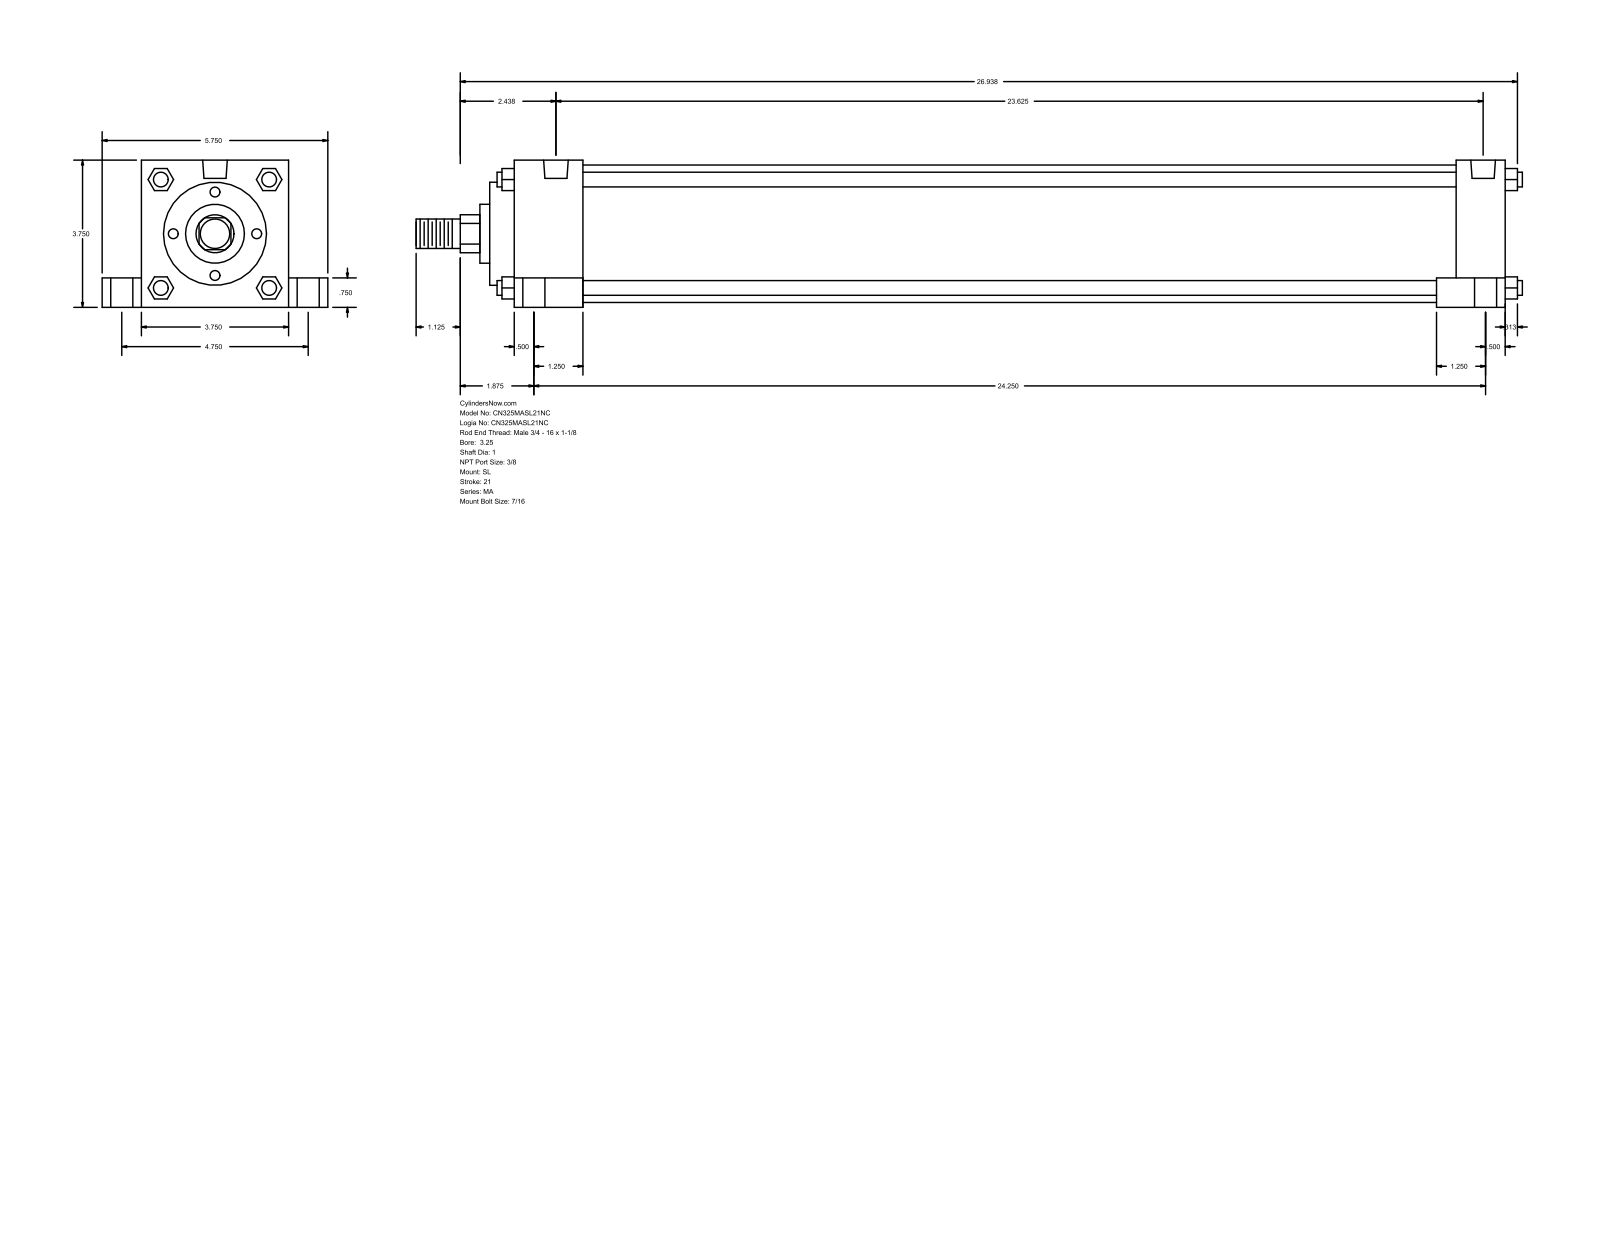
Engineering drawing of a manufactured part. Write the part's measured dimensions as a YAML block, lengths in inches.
part_name: "MA_SL__0325_1"
step_written_by: "GSSL Pune (CONFIG_CONTROL_DESIGN)"
units: inches
bodies: {solids: 0, faces: 150, planar: 113, cylindrical: 37, other: 0}
overall_size: [28.187, 5.75, 3.75]
round_holes:
  - {diameter: 0.437, count: 4}
  - {diameter: 0.563, count: 4}
  - {diameter: 0.813, count: 4}
  - {diameter: 0.627, count: 2}
round_bosses_or_shafts:
  - {diameter: 0.375, count: 4}
  - {diameter: 3.5, count: 1}
  - {diameter: 2.625, count: 1}
  - {diameter: 1.5, count: 1}
  - {diameter: 1, count: 1}
  - {diameter: 0.75, count: 1}
partial_cylinders:
  - {radius: 0.484, count: 1}
face_to_face_distances: [3.75, 25.25, 0.625, 1, 4.75, 25.875, 0.75, 24, 1.25, 1.75]
hole_center_spacings: [0.187, 2.376, 2.388, 2.441, 2.491, 4.75, 23.25, 23.438]
